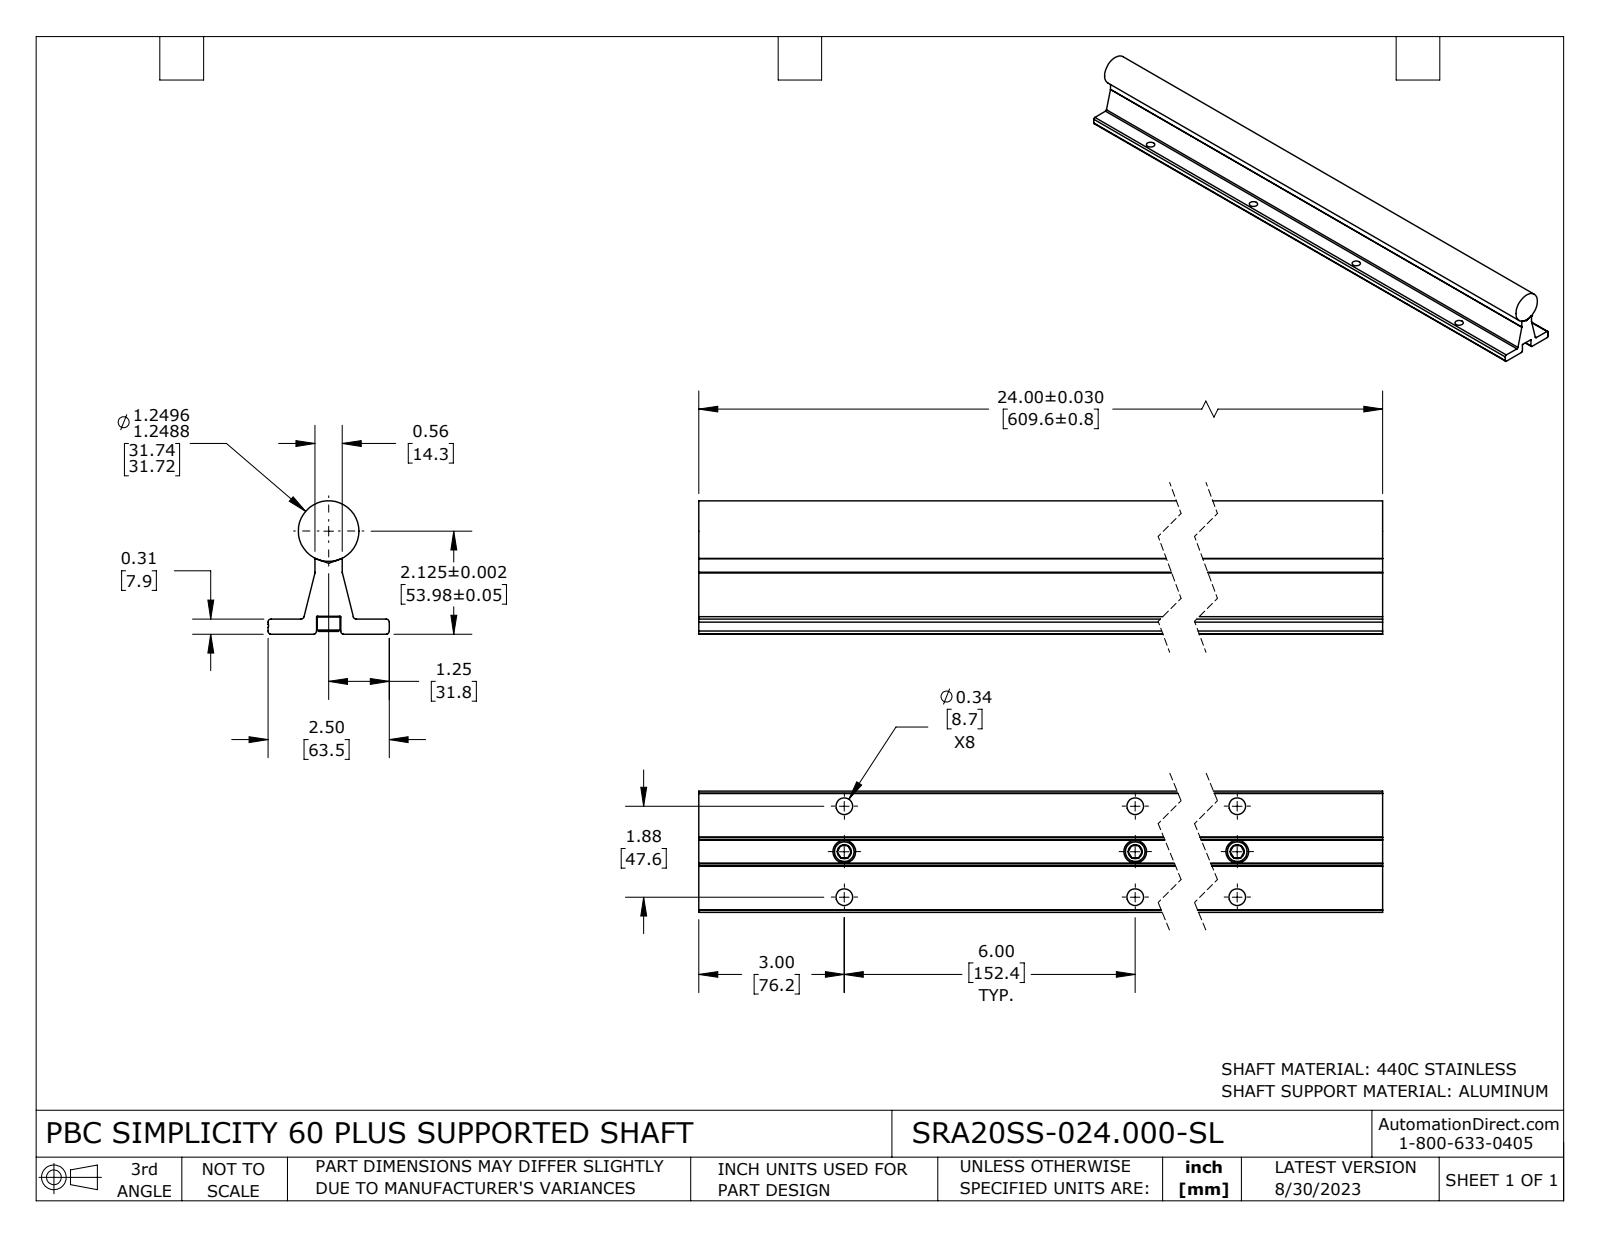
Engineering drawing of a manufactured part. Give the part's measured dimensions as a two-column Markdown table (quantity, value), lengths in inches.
| quantity | value |
| --- | --- |
| part name | SRA20SS-024.000-SL |
| STEP written by | SolidWorks 2021 (CONFIG_CONTROL_DESIGN) |
| units | inches |
| bodies | 6 solids, 203 faces (71 planar, 72 cylindrical, 60 other) |
| overall size | 24 × 2.75 × 2.5 |
| volume | 65.16 in³ |
| surface area | 317.6 in² |
| round holes (diameter × count) | 0.344 × 12, 0.272 × 4, 0.375 × 4 |
| round bosses / shafts (diameter × count) | 0.469 × 4, 0.313 × 4, 1.25 × 1 |
| partial cylindrical surfaces (radius × count) | 0.063 × 6, 0.062 × 3, 0.015 × 2, 0.033 × 2, 0.063 × 1 |
| main face-to-face distances | 0.313, 0.031, 0.531, 0.367, 0.055, 0.969, 1, 1.5, 1.531, 0.5 |
| hole center spacings | 6.073, 6, 0.937, 12.037, 6.286, 12, 1.875, 12.146 |
